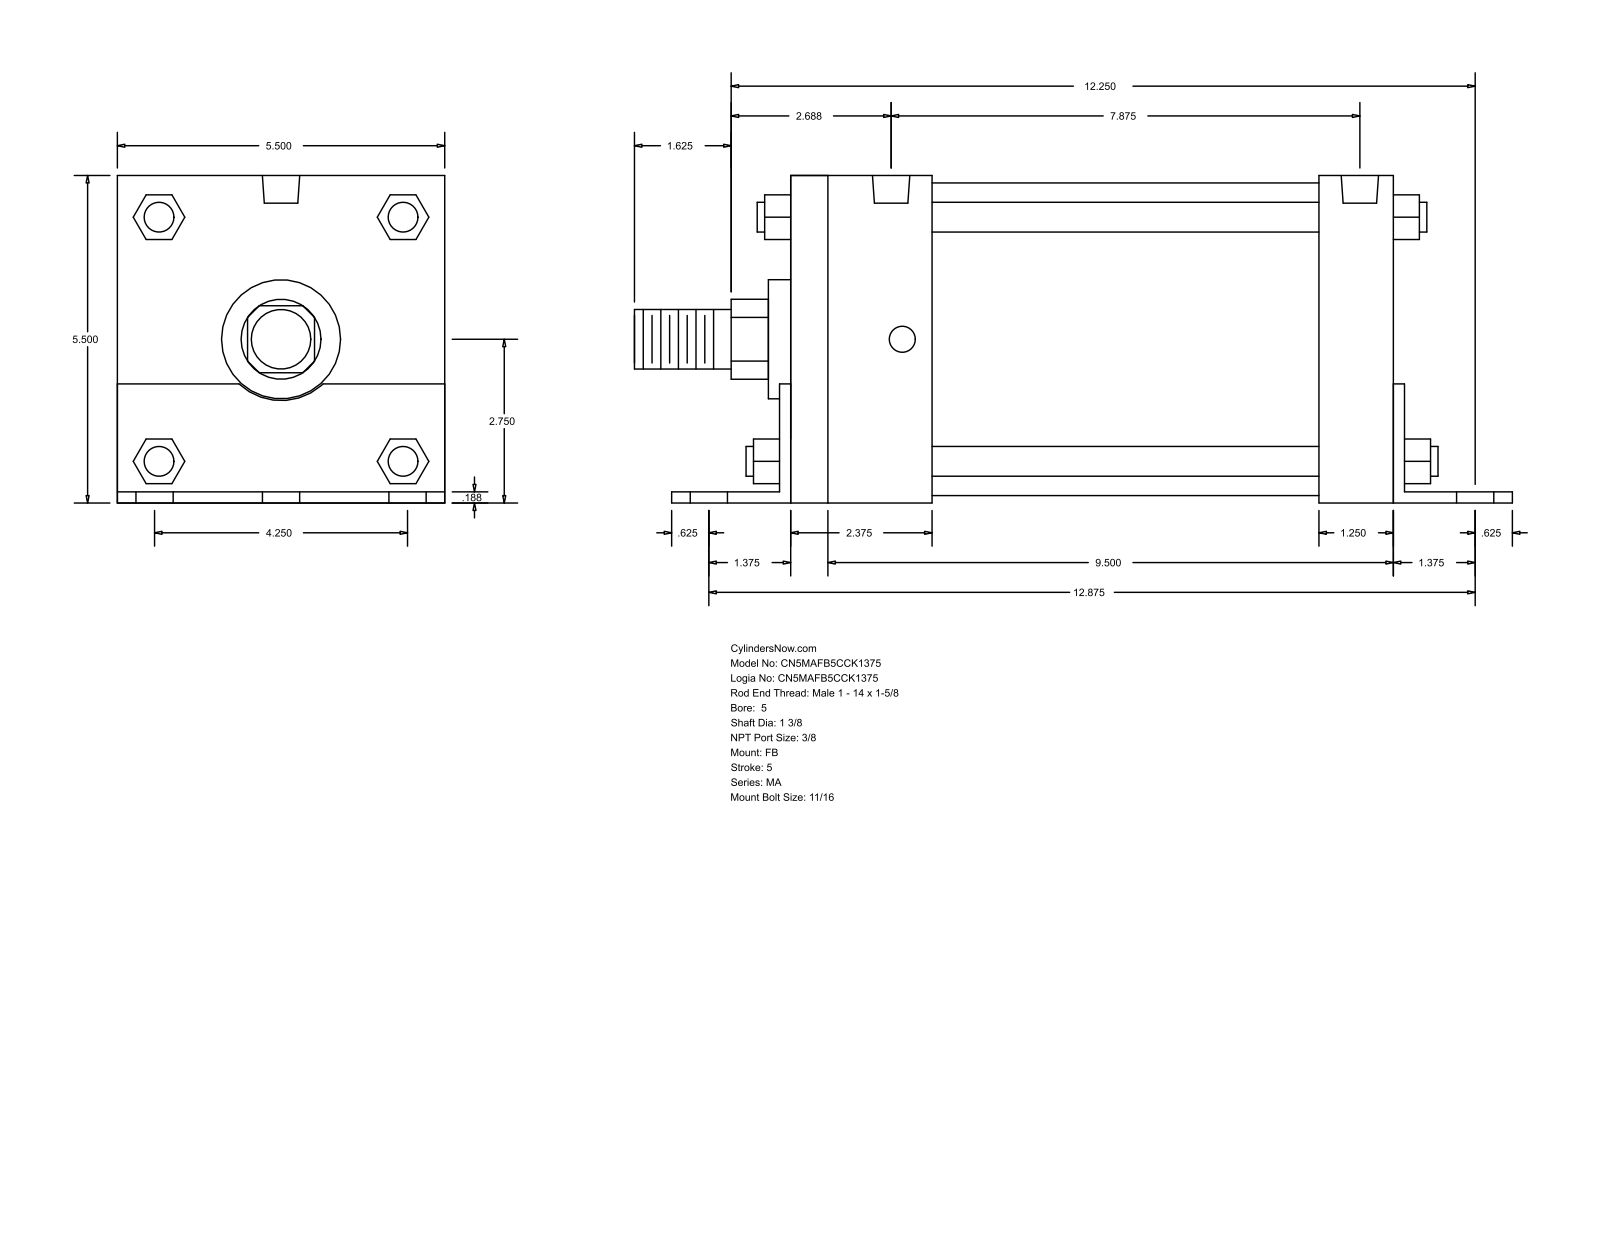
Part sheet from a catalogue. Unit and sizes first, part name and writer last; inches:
Units: inches
Overall size (bounding box): 14.75 × 5.502 × 5.5
Round holes (diameter × count): ⌀0.687 ×6, ⌀0.437 ×4, ⌀0.627 ×2
Round bosses / shafts (diameter × count): ⌀0.5 ×4, ⌀5.25 ×1, ⌀2 ×1, ⌀1.375 ×1, ⌀1 ×1
Partial cylindrical surfaces — rounded edges, fillets, slot ends (radius × count): R0.672 ×1, R1.03 ×1
Main face-to-face distances: 5.5, 0.187, 5.502, 0.185, 5.315, 10.125, 0.188, 10.313, 10.312, 10.5
Hole centre spacings: 2.125, 13.05, 12.875, 0.188, 2.876, 3.006, 3.728, 3.883
Bodies: 0 solids, 140 faces (105 planar, 35 cylindrical, 0 other)
Part name (STEP PRODUCT): MA_FB__0500_1.375
STEP written by: GSSL Pune (CONFIG_CONTROL_DESIGN)
